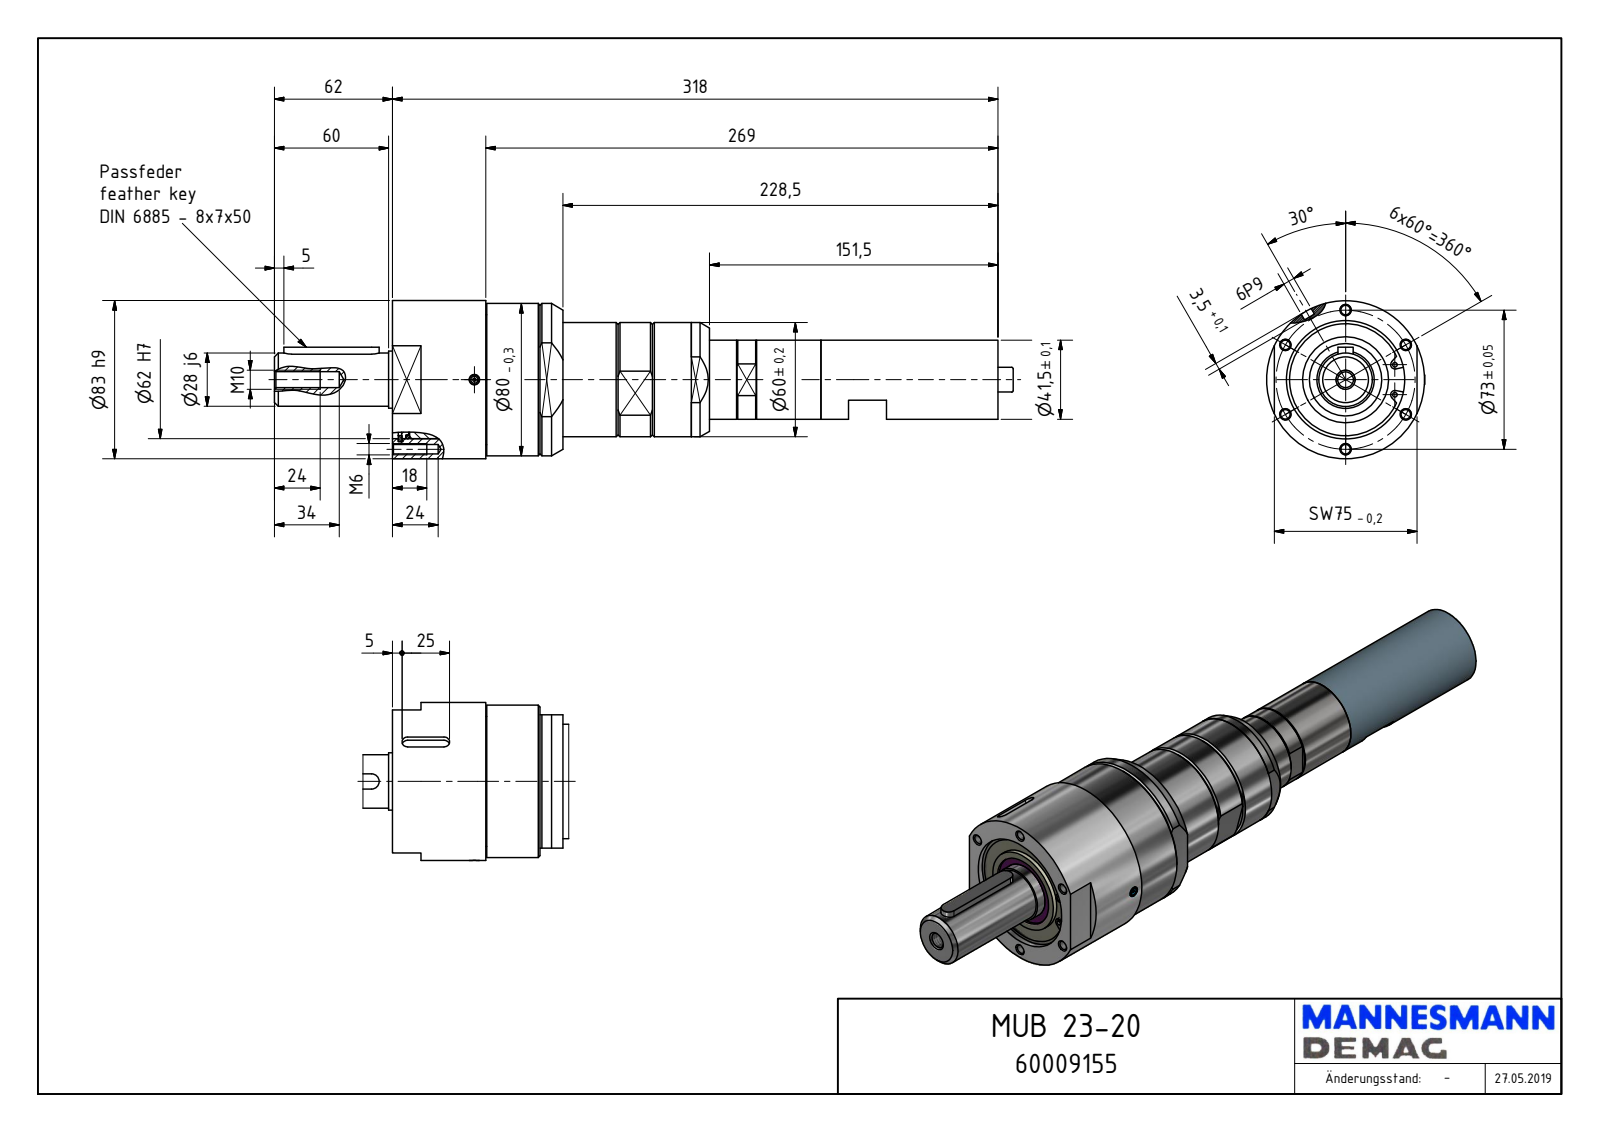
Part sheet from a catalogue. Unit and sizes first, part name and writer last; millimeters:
Units: millimetres
Overall size (bounding box): 388 × 83 × 83
Round holes (diameter × count): ⌀4.92 ×6, ⌀1.55 ×3, ⌀2.5 ×2, ⌀4 ×2, ⌀5.5 ×2, ⌀8.57 ×2, ⌀8.38 ×1, ⌀8.5 ×1, ⌀39.5 ×1, ⌀42 ×1, ⌀58.69 ×1, ⌀62 ×1
Round bosses / shafts (diameter × count): ⌀5 ×2, ⌀3.6 ×2, ⌀3.3 ×2, ⌀83 ×1, ⌀80 ×1, ⌀68.18 ×1, ⌀67 ×1, ⌀60 ×1
Partial cylindrical surfaces — rounded edges, fillets, slot ends (radius × count): R3.5 ×94, R1 ×2, R1.6 ×2, R2 ×2, R2.25 ×2, R2.5 ×2, R3 ×2, R4 ×2
Main face-to-face distances: 4.29, 49, 44.71, 228.5, 151.5, 40.5, 89.5, 85.21, 0.5, 318
Hole centre spacings: 36.5, 63.22, 73, 11.89, 26.77, 26.98, 38.53, 51.33
Volume: 895 804 mm³ · Surface area: 94 627 mm²
Bodies: 1 solid, 635 faces (193 planar, 340 cylindrical, 102 other)
Part name (STEP PRODUCT): MUB 23-20_60009155
STEP written by: Autodesk Inventor 2018 (AUTOMOTIVE_DESIGN)
